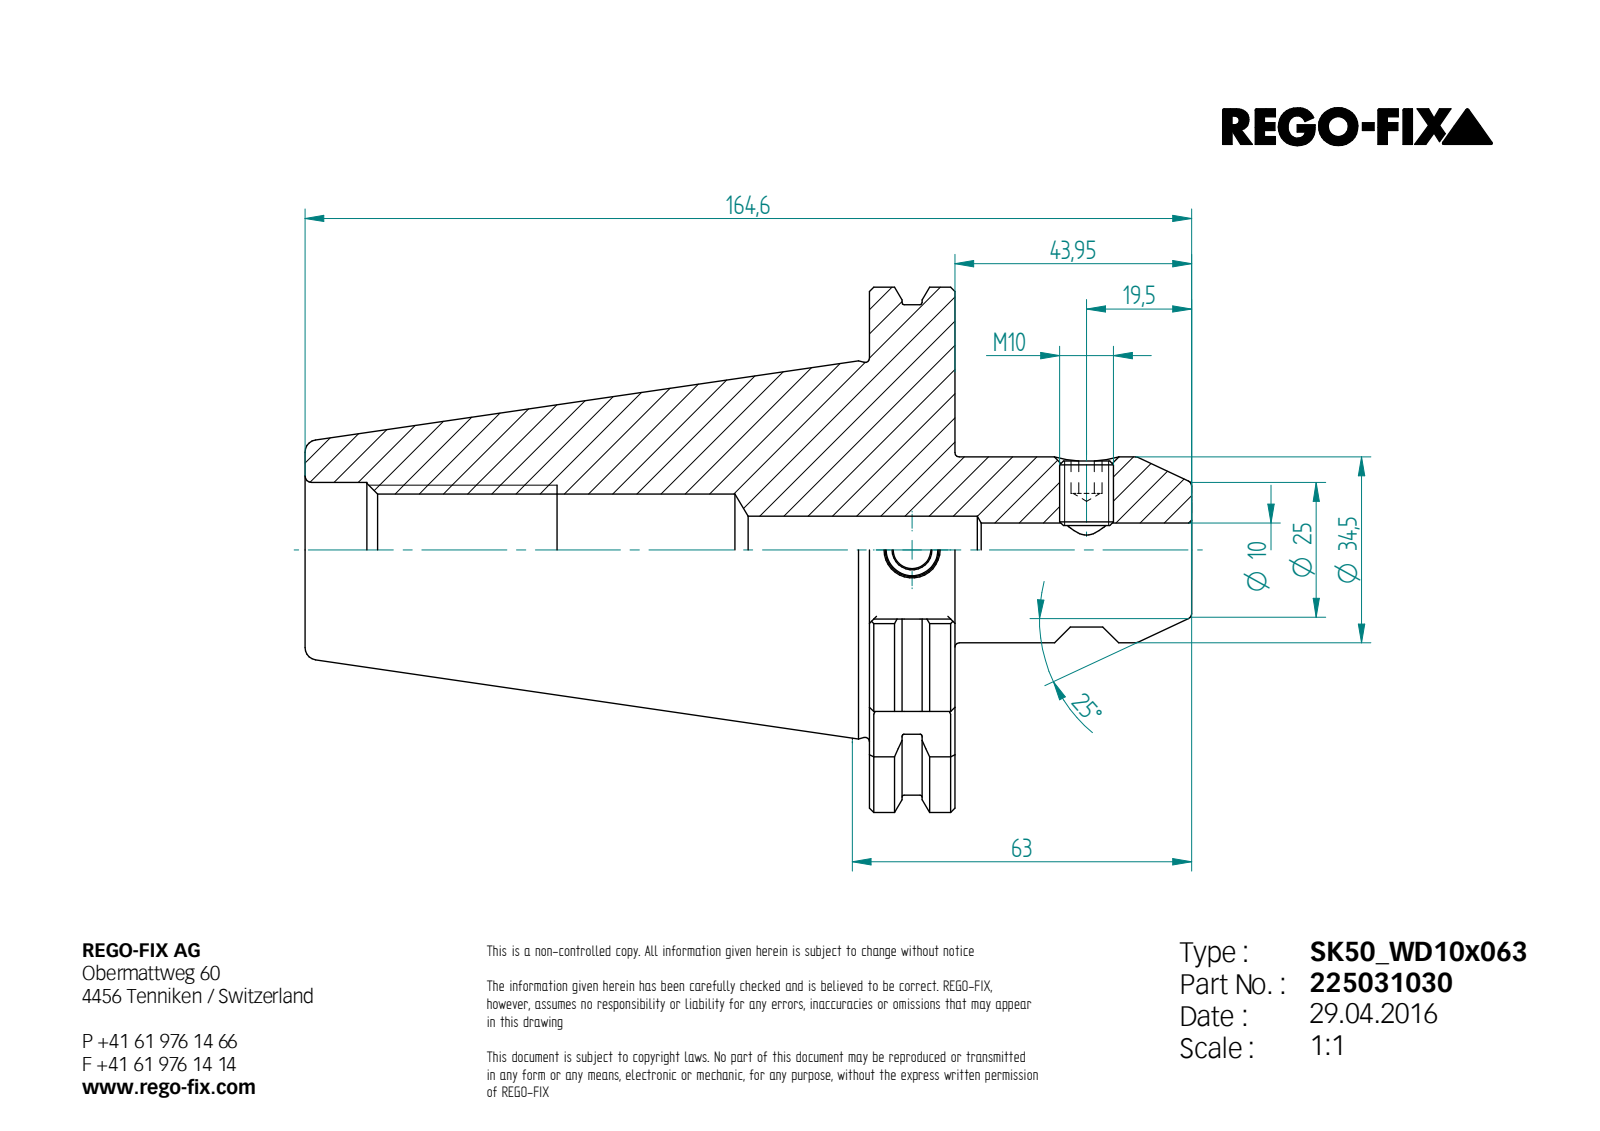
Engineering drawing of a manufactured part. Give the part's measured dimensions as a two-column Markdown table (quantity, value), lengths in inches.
| quantity | value |
| --- | --- |
| STEP written by | Unknown (AUTOMOTIVE_DESIGN) |
| units | inches |
| bodies | 2 solids, 121 faces (58 planar, 24 cylindrical, 39 other) |
| overall size | 6.48 × 3.839 × 3.684 |
| volume | 22.21 in³ |
| surface area | 75.69 in² |
| round holes (diameter × count) | 0.394 × 2, 0.276 × 1, 0.33 × 1, 0.492 × 1, 0.817 × 1, 0.984 × 1 |
| round bosses / shafts (diameter × count) | 3.583 × 1, 1.358 × 1, 0.394 × 1 |
| partial cylindrical surfaces (radius × count) | 0.02 × 5, 1.919 × 1 |
| main face-to-face distances | 0.624, 4.126, 4.75, 6.48, 2.354, 1.73, 2.866, 1.012, 0.057, 1.069 |
